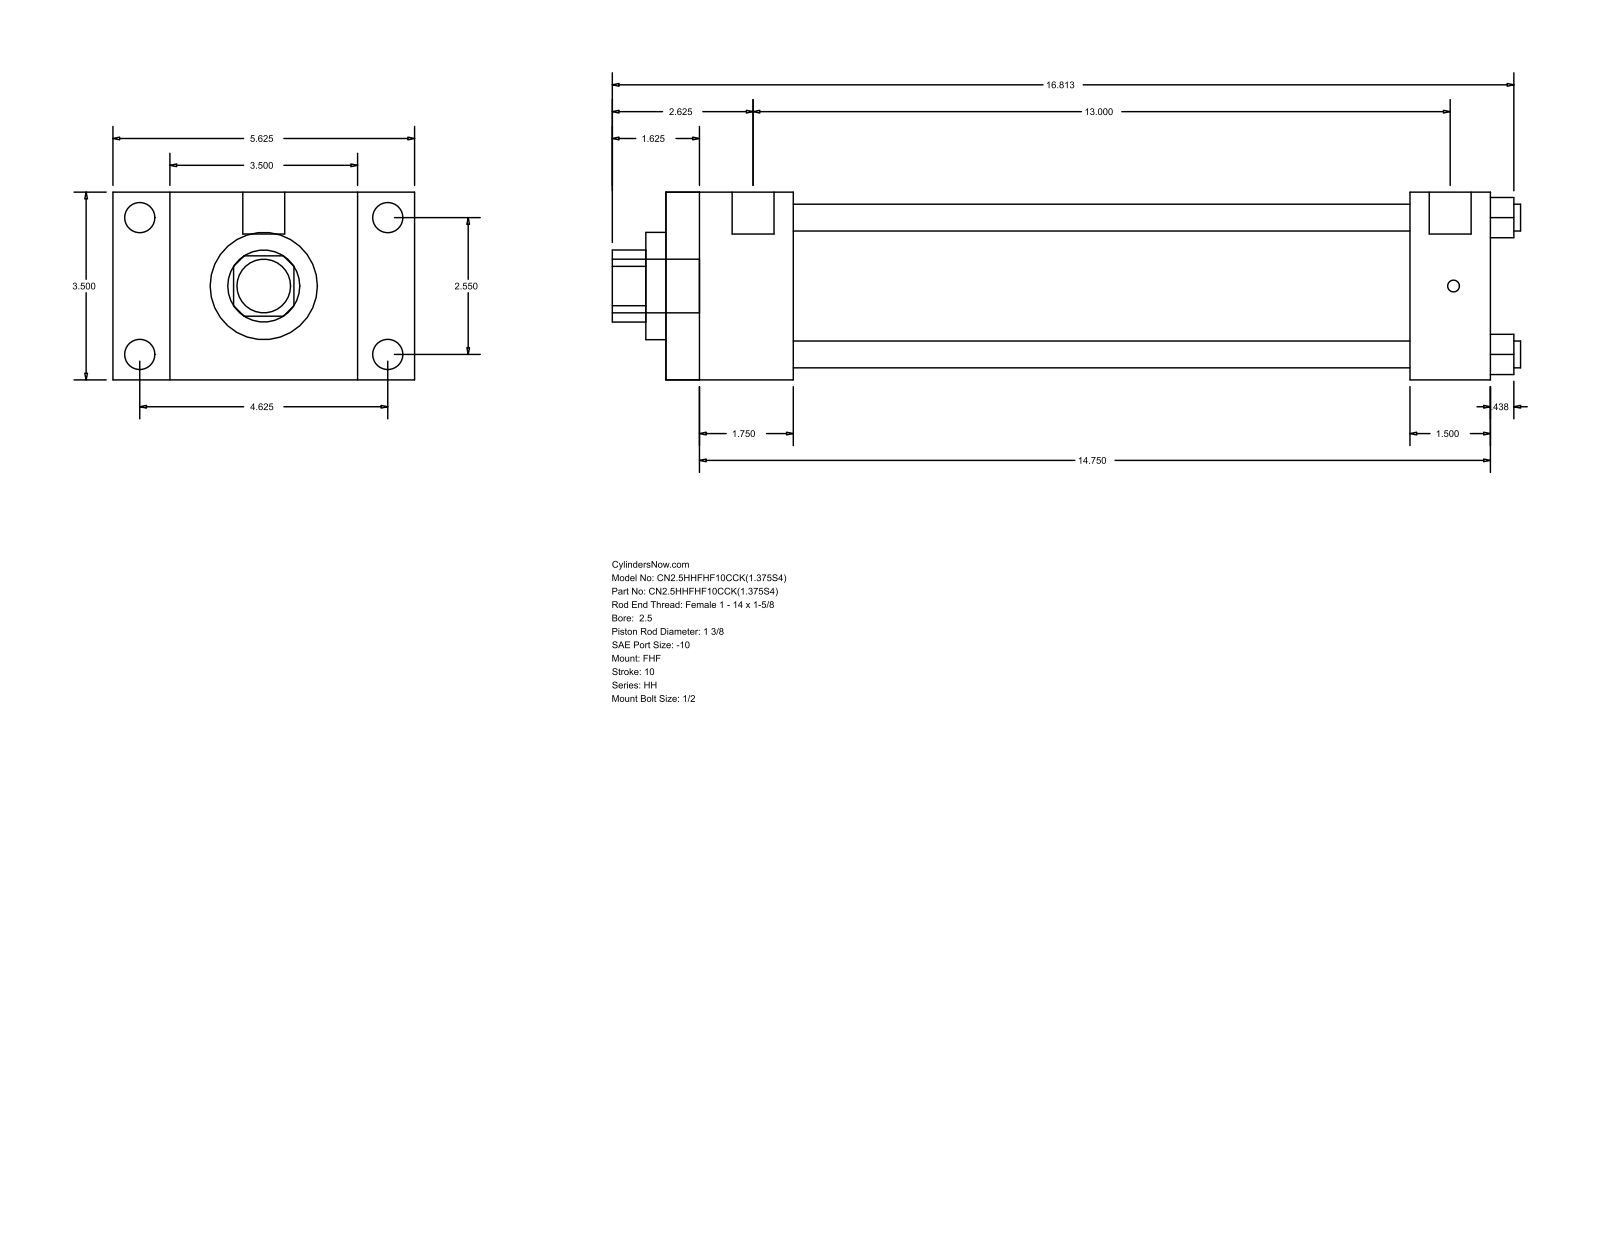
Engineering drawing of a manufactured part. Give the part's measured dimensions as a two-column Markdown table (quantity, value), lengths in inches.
| quantity | value |
| --- | --- |
| part name | HH_FHF__0250_1.375 |
| STEP written by | GSSL Pune (CONFIG_CONTROL_DESIGN) |
| units | inches |
| bodies | 0 solids, 88 faces (60 planar, 28 cylindrical, 0 other) |
| overall size | 16.937 × 5.625 × 3.5 |
| round holes (diameter × count) | 0.5 × 4, 1.375 × 1, 2 × 1, 2.875 × 1 |
| round bosses / shafts (diameter × count) | 0.563 × 4, 0.219 × 4, 0.781 × 2, 1 × 1 |
| partial cylindrical surfaces (radius × count) | 0.672 × 1 |
| main face-to-face distances | 3.5, 2.375, 1.063, 4.563, 15.375, 13, 5.625, 13.875, 11.5, 1.5 |
| hole center spacings | 1.803, 2.55, 3.606 |
